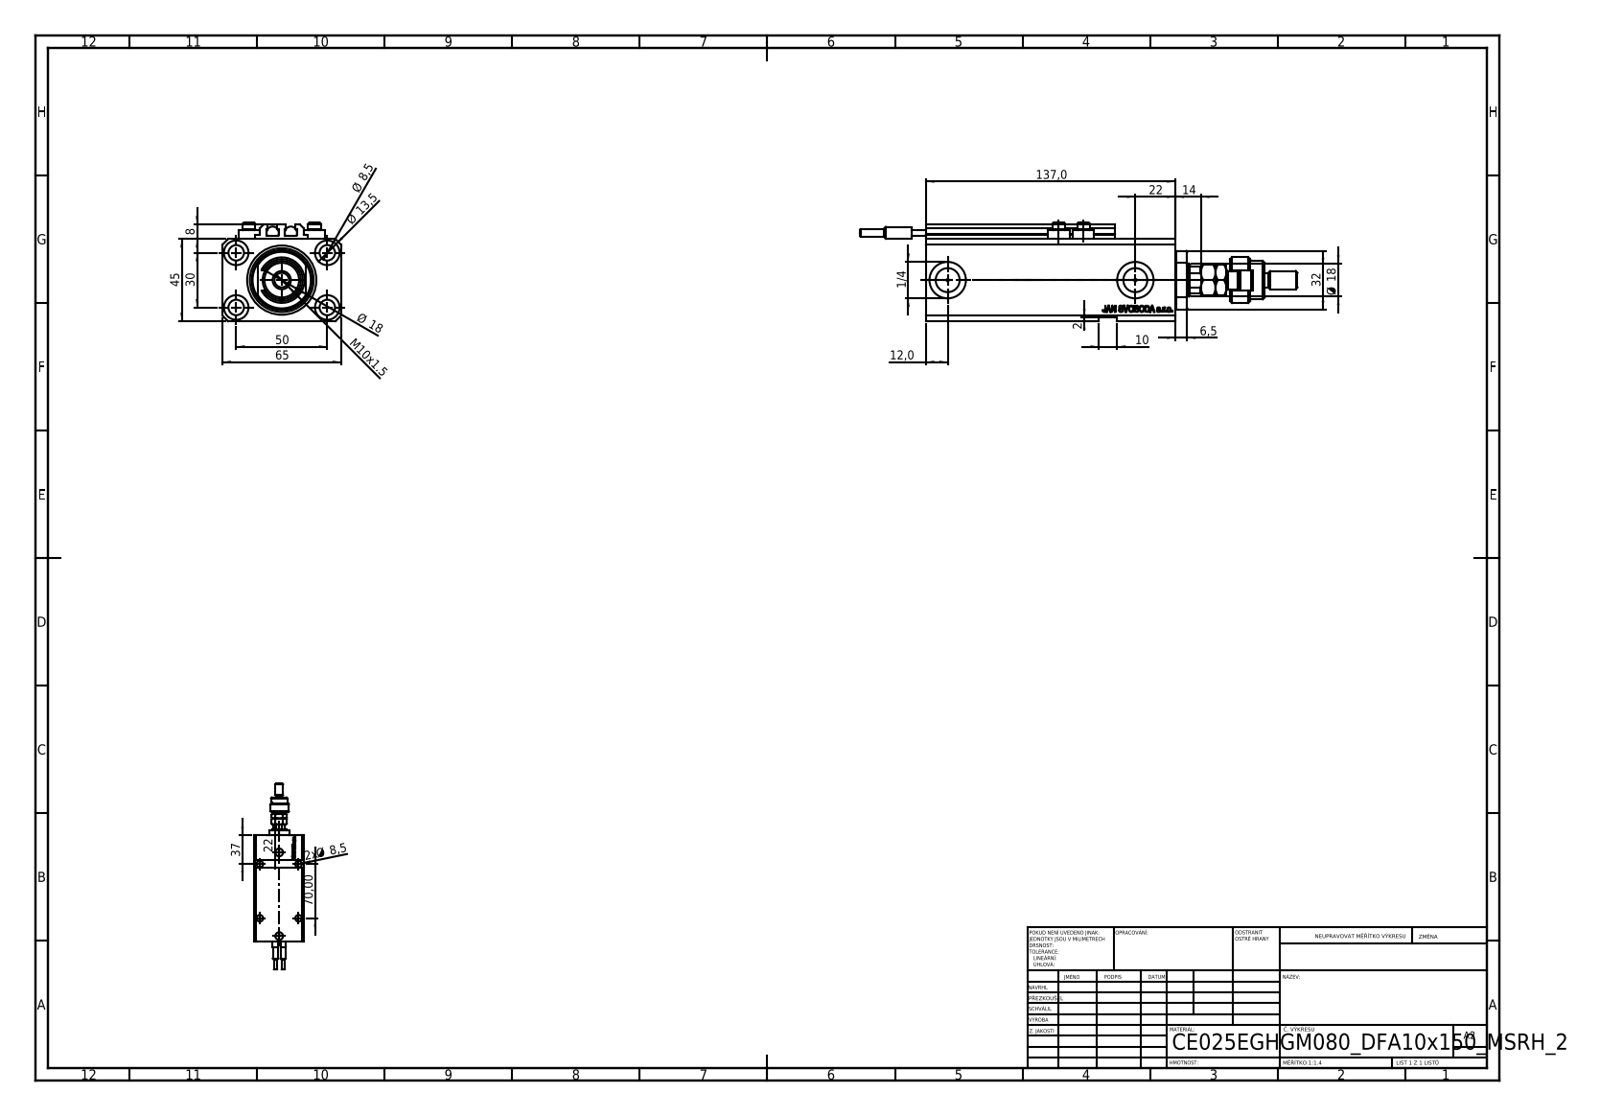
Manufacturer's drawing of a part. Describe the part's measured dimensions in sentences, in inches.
The part is named "ALLEN BOLT V250CE; FEMALE_PART_FOR_DFA; SWITCH_V250CE; V250CE_C_VCP (+3 more)". Its 3-D file was written by "SolidWorks 2019 (CONFIG_CONTROL_DESIGN)". It is 12 solids with 1224 faces: 571 planar, 171 cylindrical and 482 other. Overall it measures 9.449 by 2.559 by 2.126 inches. Its volume is 22.33 cubic inches and its surface area 157.7 square inches. Round holes: 9 of diameter 0.335, 4 of diameter 0.049, 4 of diameter 0.157, 4 of diameter 0.531, 2 of diameter 0.394, 2 of diameter 0.518, 2 of diameter 0.787, 1 of diameter 0.709, 1 of diameter 1.496. Round bosses or shafts: 4 of diameter 0.457, 4 of diameter 0.276, 2 of diameter 0.268, 2 of diameter 0.256, 2 of diameter 0.157, 1 of diameter 0.984, 1 of diameter 0.827, 1 of diameter 0.63. Partial cylindrical surfaces (rounded edges, fillets, slot ends): 10 of radius 0.008, 1 of radius 0.217, 1 of radius 0.335, 1 of radius 0.344, 1 of radius 0.63. The main face-to-face distances are 1.772, 2.559, 0.551, 0.079, 1.85, 0.118, 0.098, 4.843, 0.394, 5.394. The hole center spacings are 1.148, 1.969, 0.535, 0.595, 1.098, 1.181, 1.323, 1.324.
